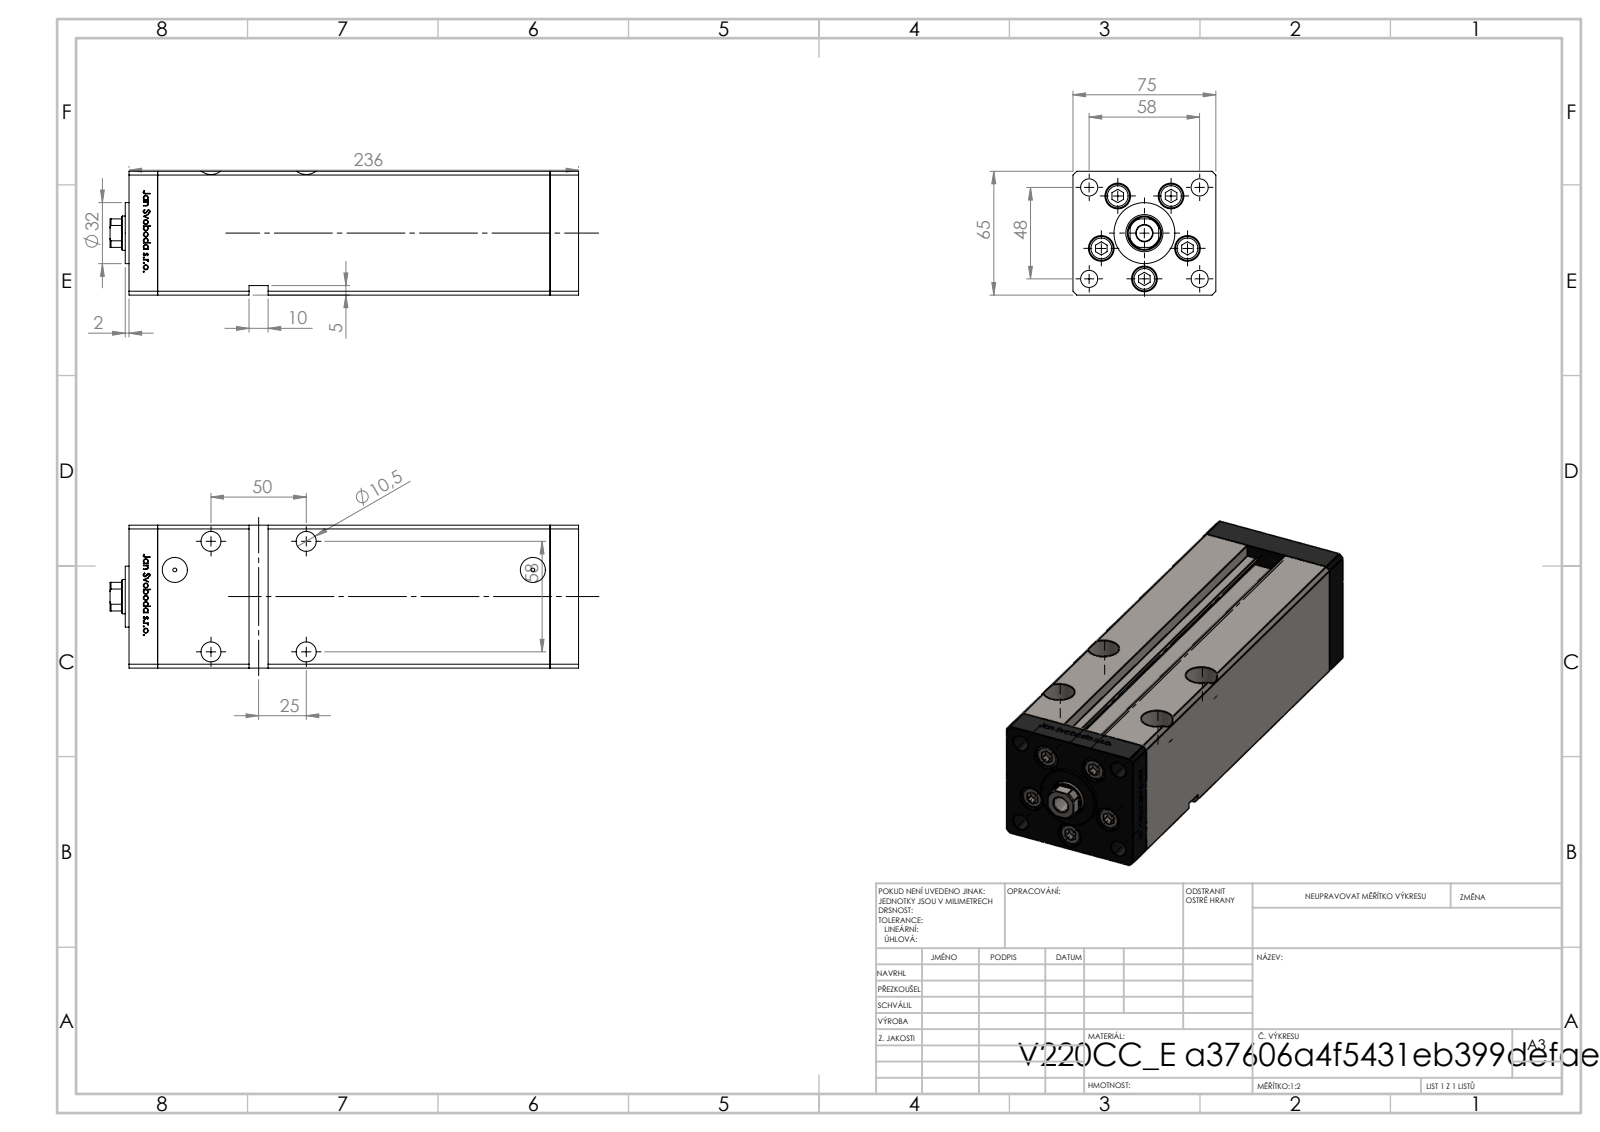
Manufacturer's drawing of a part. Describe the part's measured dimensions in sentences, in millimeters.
The part is named "V220C_E MIDDLE; ALLEN BOLT; V220C_FRONT_E; V220C_VC_E (+1 more)". Its 3-D file was written by "SolidWorks 2019 (CONFIG_CONTROL_DESIGN)". It is 14 solids with 1212 faces: 473 planar, 165 cylindrical and 574 other. Overall it measures 246 by 75 by 65 millimeters. Its volume is 975 804 cubic millimeters and its surface area 169 473 square millimeters. Round holes: 9 of diameter 9, 5 of diameter 13.5, 4 of diameter 10.5, 4 of diameter 16.5, 2 of diameter 2, 2 of diameter 13.16, 1 of diameter 8.5, 1 of diameter 18, 1 of diameter 19.5. Round bosses or shafts: 5 of diameter 12.5, 5 of diameter 8, 1 of diameter 32. Partial cylindrical surfaces (rounded edges, fillets, slot ends): 2 of radius 0.93, 1 of radius 8.5. The main face-to-face distances are 75, 65, 15, 206, 221, 236, 54.5, 10.5, 26.25, 48.75. The hole center spacings are 24, 37.64, 58, 15.67, 17.22, 27.71, 28.83, 29.
